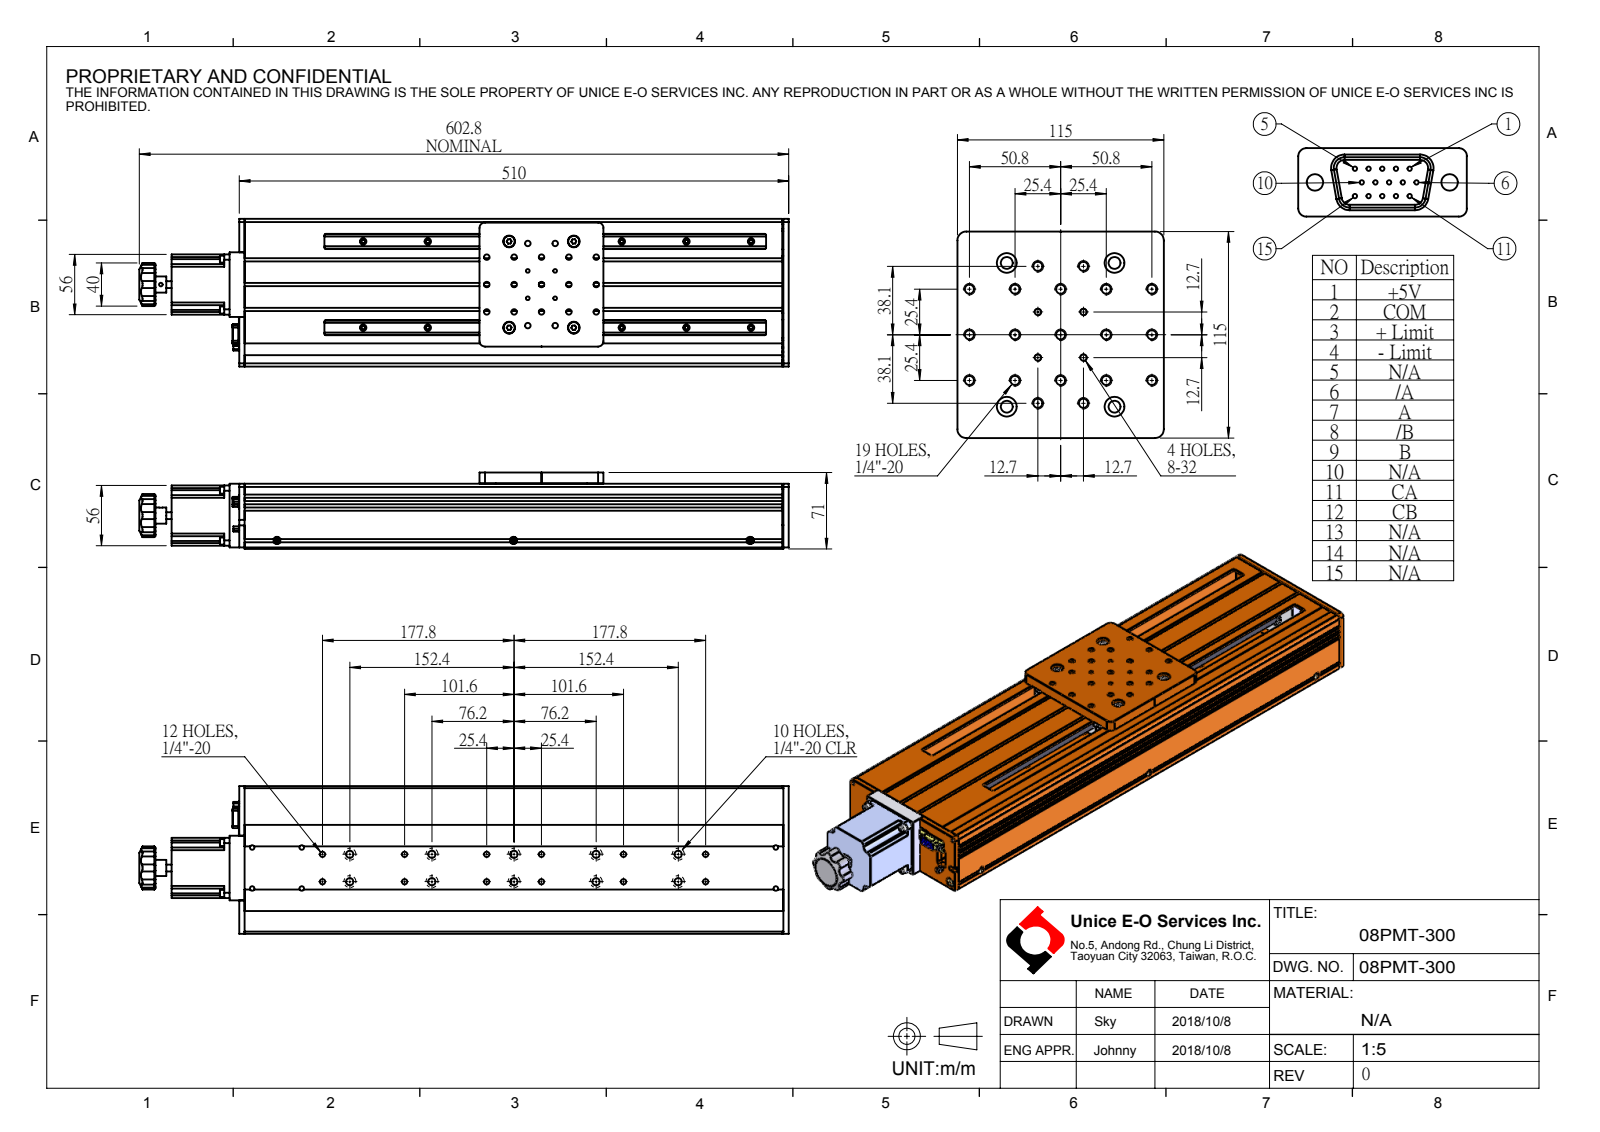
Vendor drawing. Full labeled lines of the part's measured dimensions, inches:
Part name (STEP PRODUCT): 08PMT-300
STEP written by: SolidWorks 2016 (AUTOMOTIVE_DESIGN)
Units: inches
Bodies: 0 solids, 781 faces (370 planar, 289 cylindrical, 122 other)
Overall size (bounding box): 23.732 × 5.394 × 2.795
Round holes (diameter × count): ⌀0.201 ×19, ⌀0.197 ×12, ⌀0.266 ×10, ⌀0.437 ×10, ⌀0.031 ×7, ⌀0.165 ×6, ⌀0.039 ×5, ⌀0.136 ×4, ⌀0.433 ×4, ⌀0.079 ×2, ⌀0.098 ×2, ⌀0.13 ×2
Round bosses / shafts (diameter × count): ⌀0.256 ×4, ⌀0.228 ×3, ⌀0.118 ×3, ⌀0.303 ×2, ⌀0.63 ×1, ⌀0.591 ×1, ⌀0.25 ×1
Partial cylindrical surfaces — rounded edges, fillets, slot ends (radius × count): R0.059 ×10, R0.079 ×8, R0.157 ×8, R0.197 ×8, R0.292 ×8, R0.02 ×7, R0.177 ×4, R0.118 ×2
Main face-to-face distances: 0.079, 2.382, 5.315, 5.236, 0.413, 0.059, 0.354, 2.323, 5.394, 0.067
Hole centre spacings: 1, 3, 3.162, 1.414, 4, 4.123, 7, 7.071
